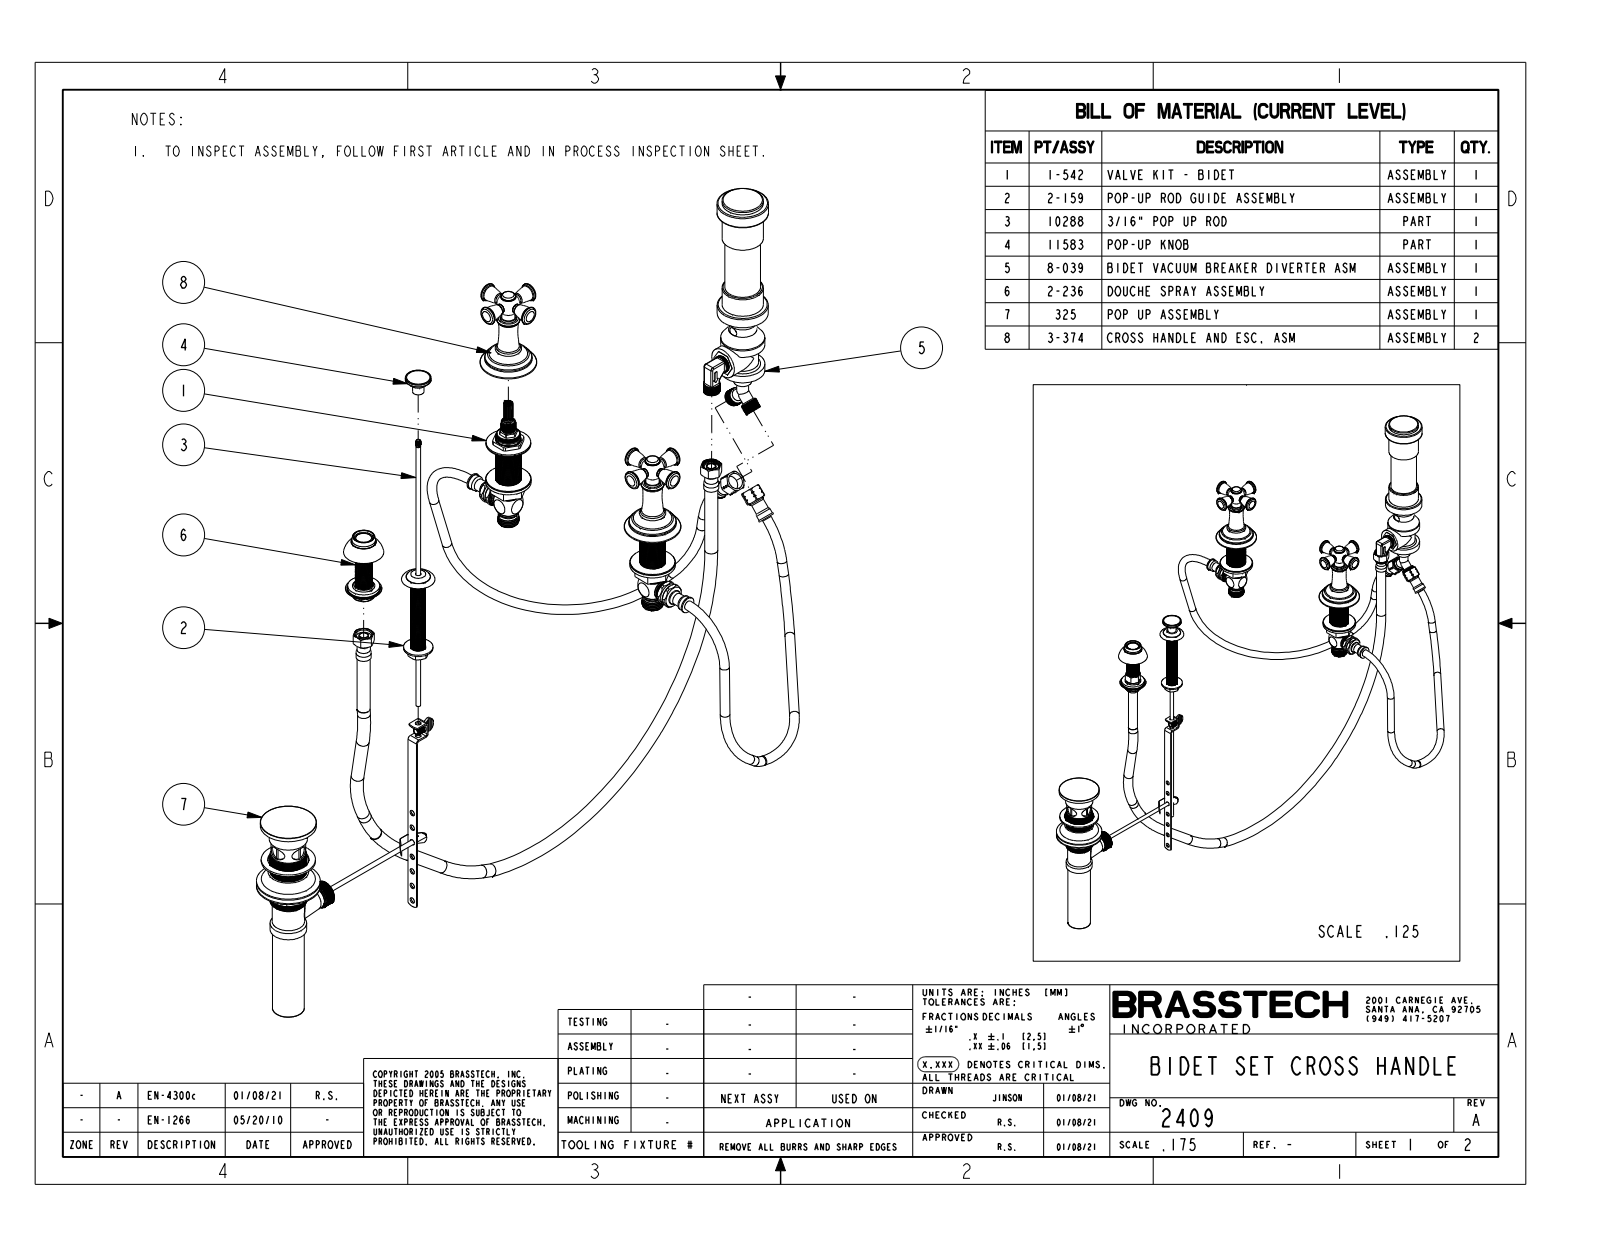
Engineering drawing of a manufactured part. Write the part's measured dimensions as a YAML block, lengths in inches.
part_name: "2409"
step_written_by: "CREO PARAMETRIC BY PTC INC, 2018400 (CONFIG_CONTROL_DESIGN)"
units: inches
bodies: {solids: 5, faces: 383, planar: 61, cylindrical: 82, other: 240}
overall_size: [22.798, 10.528, 5.445]
volume: 19.49
surface_area: 95.76
round_holes:
  - {diameter: 0.625, count: 1}
  - {diameter: 0.792, count: 1}
  - {diameter: 0.94, count: 1}
round_bosses_or_shafts:
  - {diameter: 0.72, count: 3}
  - {diameter: 0.36, count: 3}
  - {diameter: 0.9, count: 2}
  - {diameter: 0.649, count: 2}
  - {diameter: 0.56, count: 2}
  - {diameter: 0.517, count: 2}
  - {diameter: 2.02, count: 1}
  - {diameter: 2, count: 1}
partial_cylinders:
  - {radius: 0.357, count: 1}
face_to_face_distances: [5.445, 0.5, 5.295, 0.15, 4.795, 0.65, 0.42, 4.375, 4.875, 5.025]
